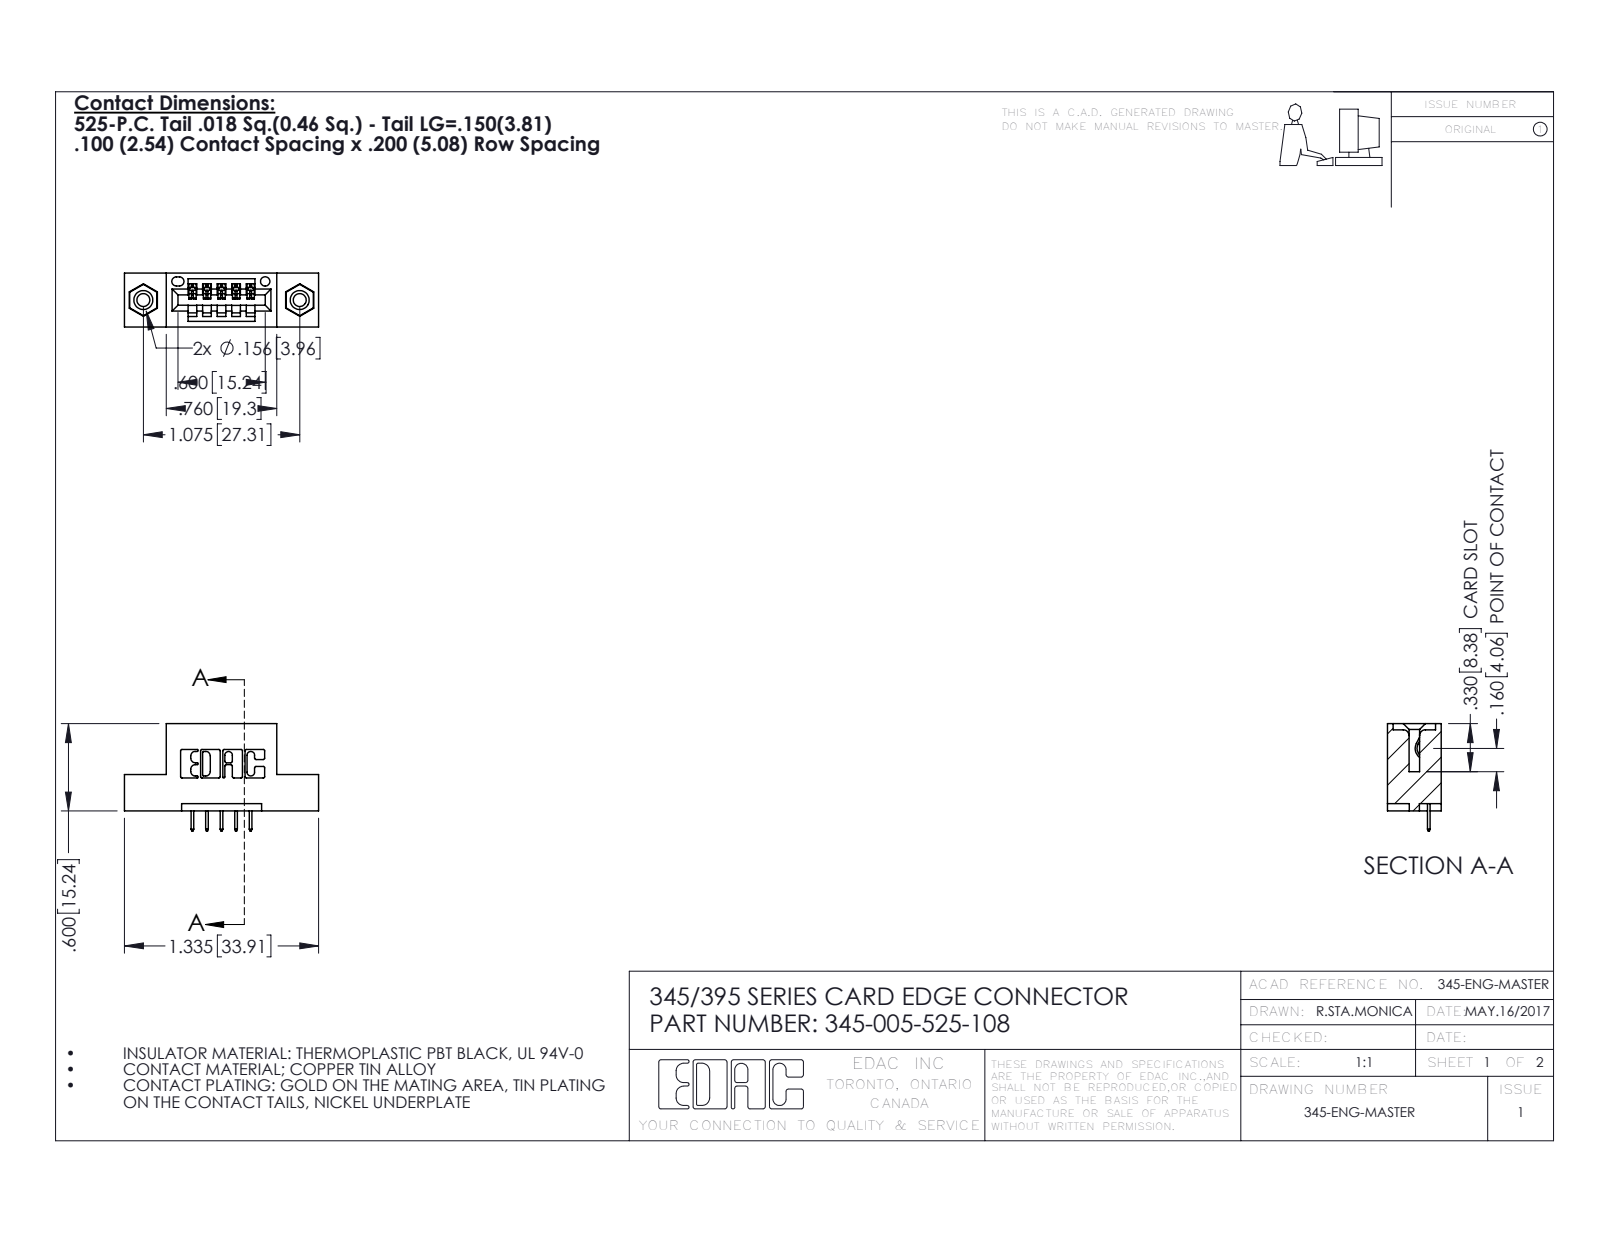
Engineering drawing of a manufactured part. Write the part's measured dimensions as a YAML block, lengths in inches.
part_name: "345 Part_Flush Mounting Lugs - 0.156 Dia-TI; 345-292-001_345-293-125; 345-250-001_345-250-003-102; 345-005-525-108"
step_written_by: "SolidWorks 2020 (CONFIG_CONTROL_DESIGN)"
units: inches
bodies: {solids: 8, faces: 496, planar: 342, cylindrical: 138, other: 16}
overall_size: [1.335, 0.737, 0.37]
volume: 0.176
surface_area: 5.099
round_holes:
  - {diameter: 0.089, count: 2}
  - {diameter: 0.125, count: 2}
  - {diameter: 0.156, count: 2}
  - {diameter: 0.064, count: 1}
round_bosses_or_shafts:
  - {diameter: 0.155, count: 2}
partial_cylinders:
  - {radius: 0.01, count: 22}
  - {radius: 0.006, count: 10}
  - {radius: 0.007, count: 6}
  - {radius: 0.031, count: 6}
  - {radius: 0.026, count: 3}
  - {radius: 0.031, count: 2}
  - {radius: 0.04, count: 2}
  - {radius: 0.014, count: 1}
face_to_face_distances: [0.2, 0.37, 0.1, 0.072, 0.298, 0.35, 0.25, 0.06, 0.55, 0.025]
hole_center_spacings: [0.27, 0.847, 1.075]
